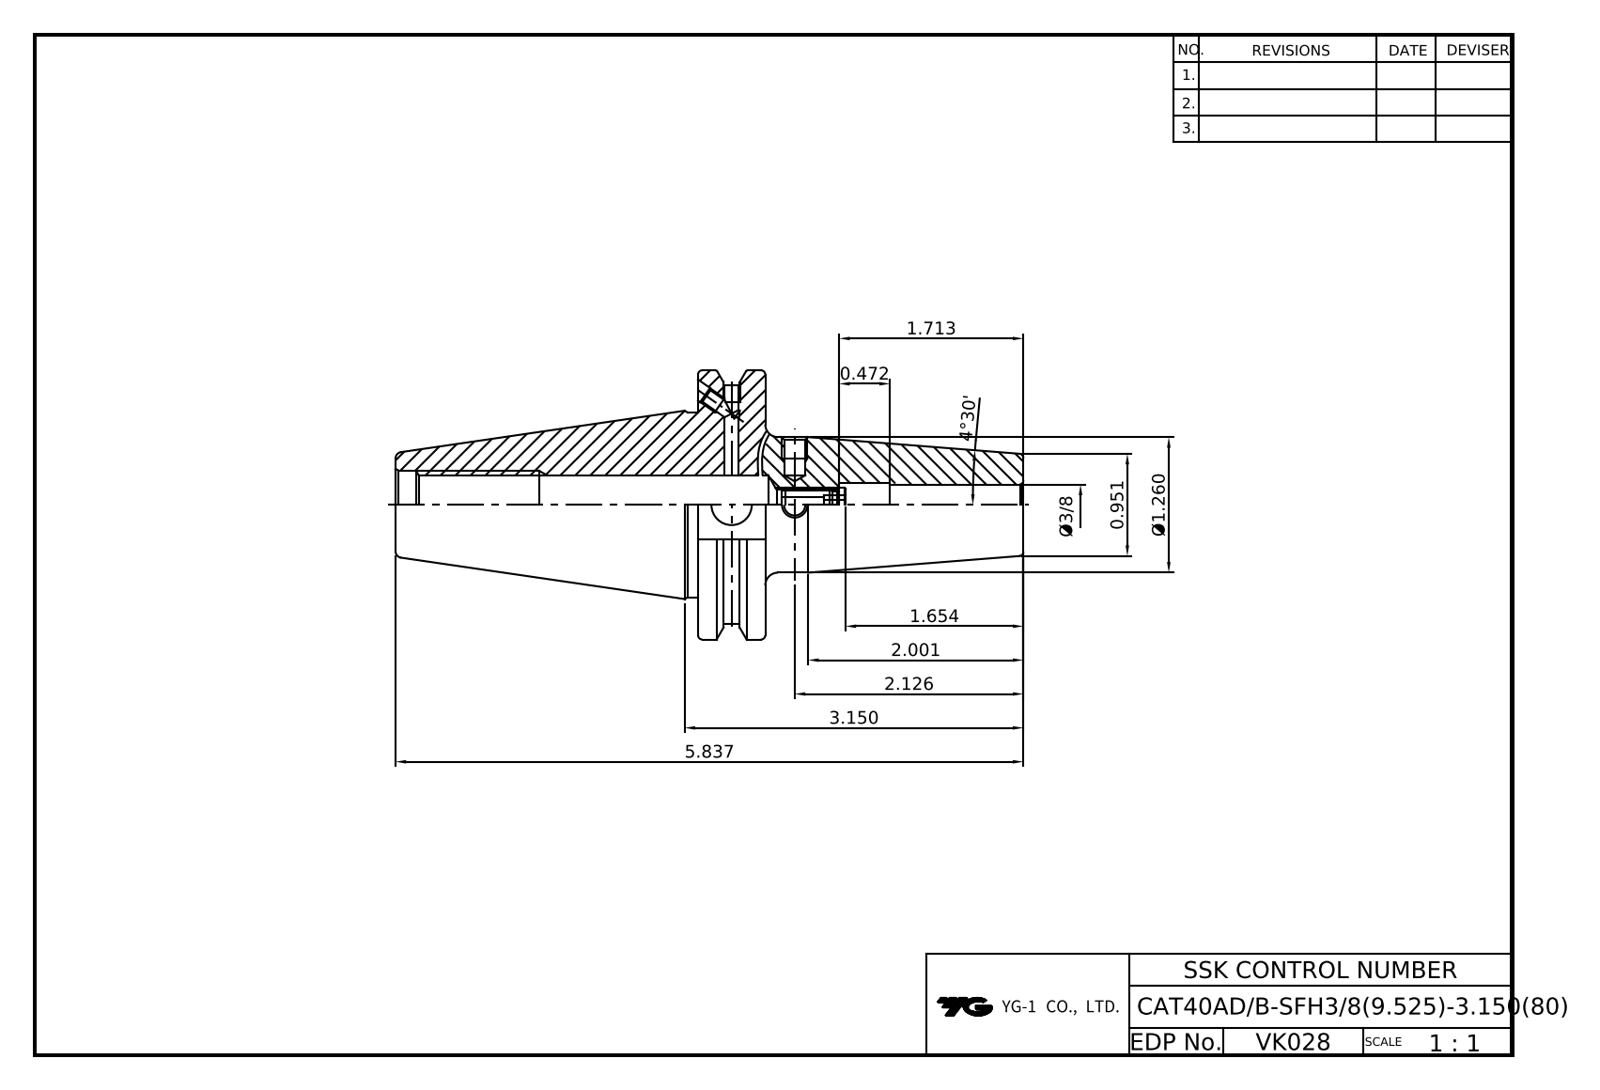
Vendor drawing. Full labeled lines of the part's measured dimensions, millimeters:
Part name (STEP PRODUCT): LO-CAT40ADB-SFH9.525-80
STEP written by: Autodesk Inventor 2025 (AUTOMOTIVE_DESIGN)
Units: millimetres
Bodies: 1 solid, 86 faces (37 planar, 28 cylindrical, 21 other)
Overall size (bounding box): 148.25 × 63.5 × 61.09
Volume: 136 563 mm³ · Surface area: 27 580 mm²
Round holes (diameter × count): ⌀3.24 ×4, ⌀4 ×2, ⌀4.2 ×2, ⌀6.92 ×1, ⌀9.52 ×1, ⌀9.53 ×1, ⌀10.72 ×1, ⌀13.39 ×1, ⌀16.3 ×1
Round bosses / shafts (diameter × count): ⌀63.5 ×1, ⌀43.6 ×1, ⌀32 ×1
Partial cylindrical surfaces — rounded edges, fillets, slot ends (radius × count): R28.15 ×1
Main face-to-face distances: 15.88, 76.83, 60.95, 47.6, 16.38, 71.42, 87.3, 148.25, 77.47, 6.05
